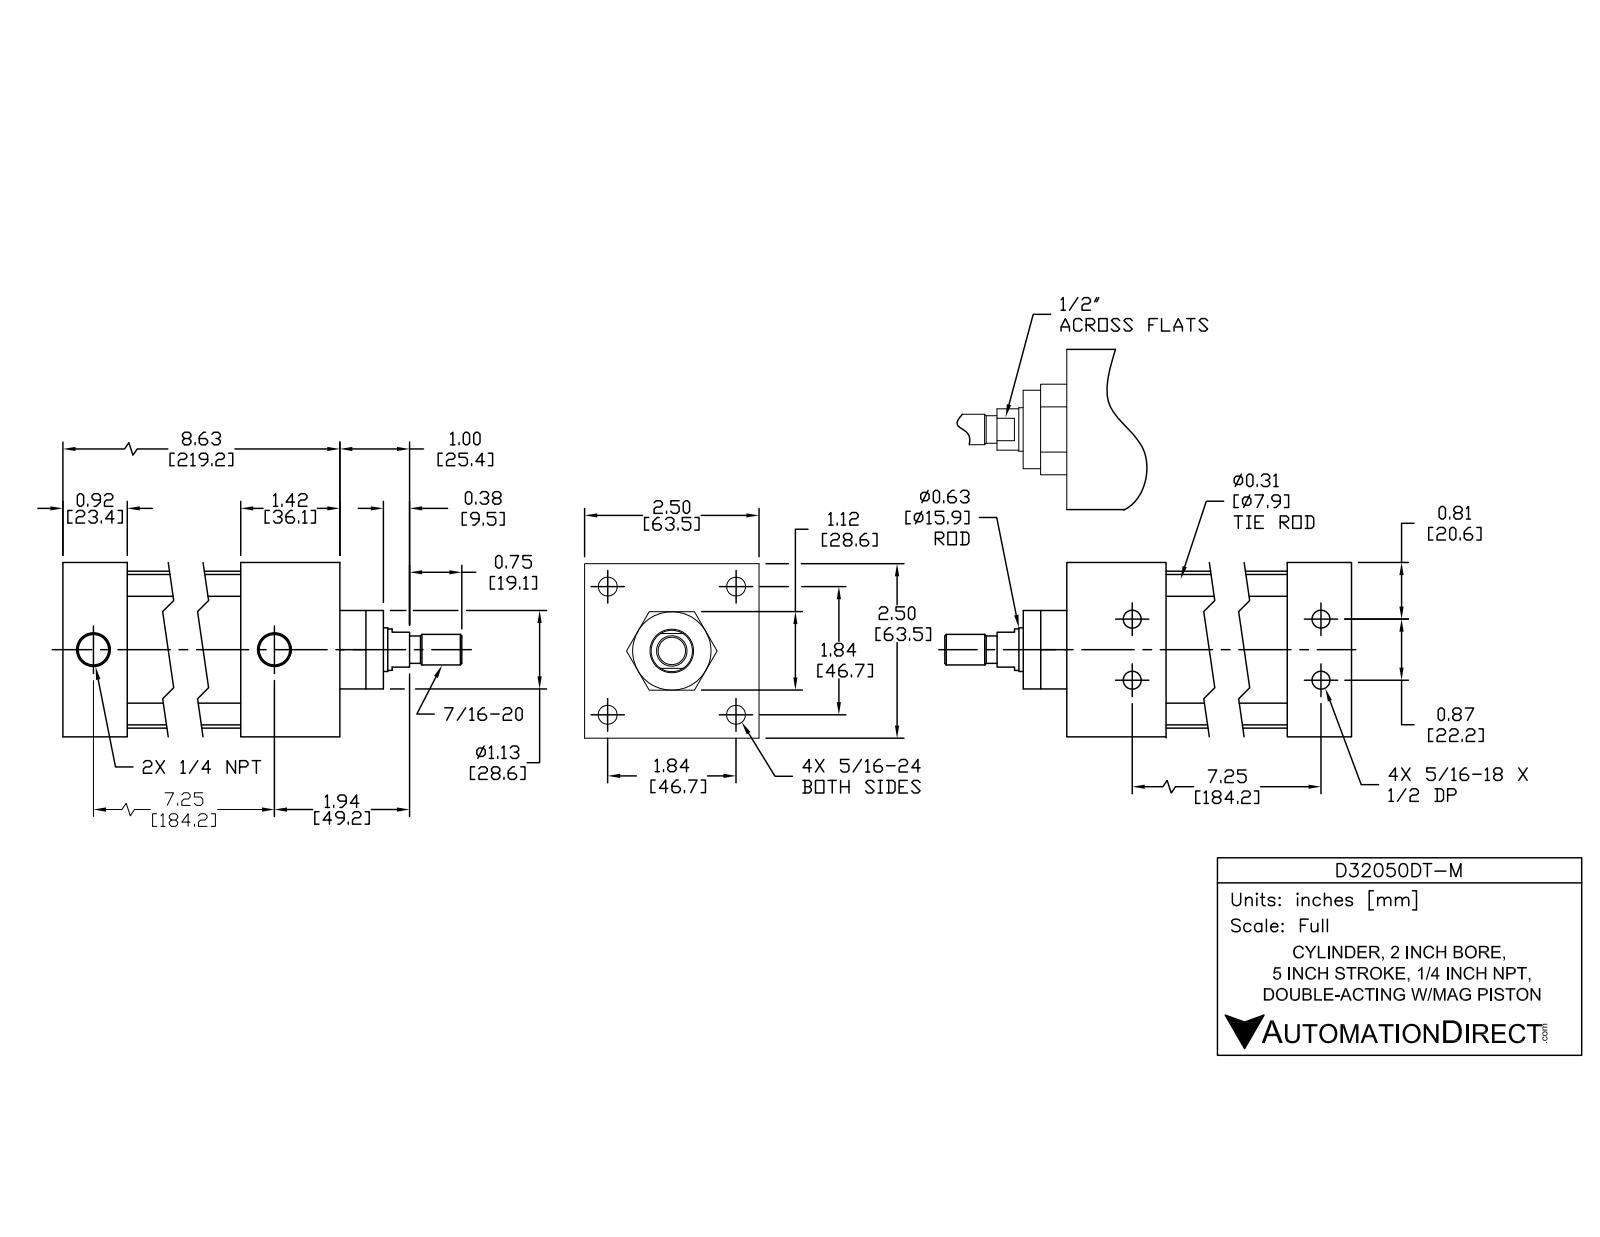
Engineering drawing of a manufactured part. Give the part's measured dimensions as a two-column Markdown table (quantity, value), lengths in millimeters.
| quantity | value |
| --- | --- |
| part name | D32050DT-M PISTON; D32050DT-M; D32050DT-M BODY |
| STEP written by | SolidWorks 2015 (AUTOMOTIVE_DESIGN) |
| units | millimeters |
| bodies | 12 solids, 298 faces (94 planar, 114 cylindrical, 90 other) |
| overall size | 263.4 × 63.5 × 63.5 |
| volume | 438 800 mm³ |
| surface area | 140 500 mm² |
| round holes (diameter × count) | 6.4 × 4, 6.8 × 4, 9.1 × 4, 12.7 × 4, 7.5 × 2, 12.1 × 2, 15.9 × 1, 16 × 1, 50.8 × 1 |
| round bosses / shafts (diameter × count) | 12.3 × 4, 8 × 4, 7.2 × 4, 57.2 × 1, 50.7 × 1, 28.4 × 1, 15.8 × 1, 15 × 1 |
| partial cylindrical surfaces (radius × count) | 6.4 × 4 |
| main face-to-face distances | 63.5, 2, 157.5, 219, 36.1, 182.9, 195.6, 159.5, 23.4, 25.4 |
| hole center spacings | 11.1, 33.2, 46.9, 184.4, 184, 22.2, 66.4, 185.4 |
